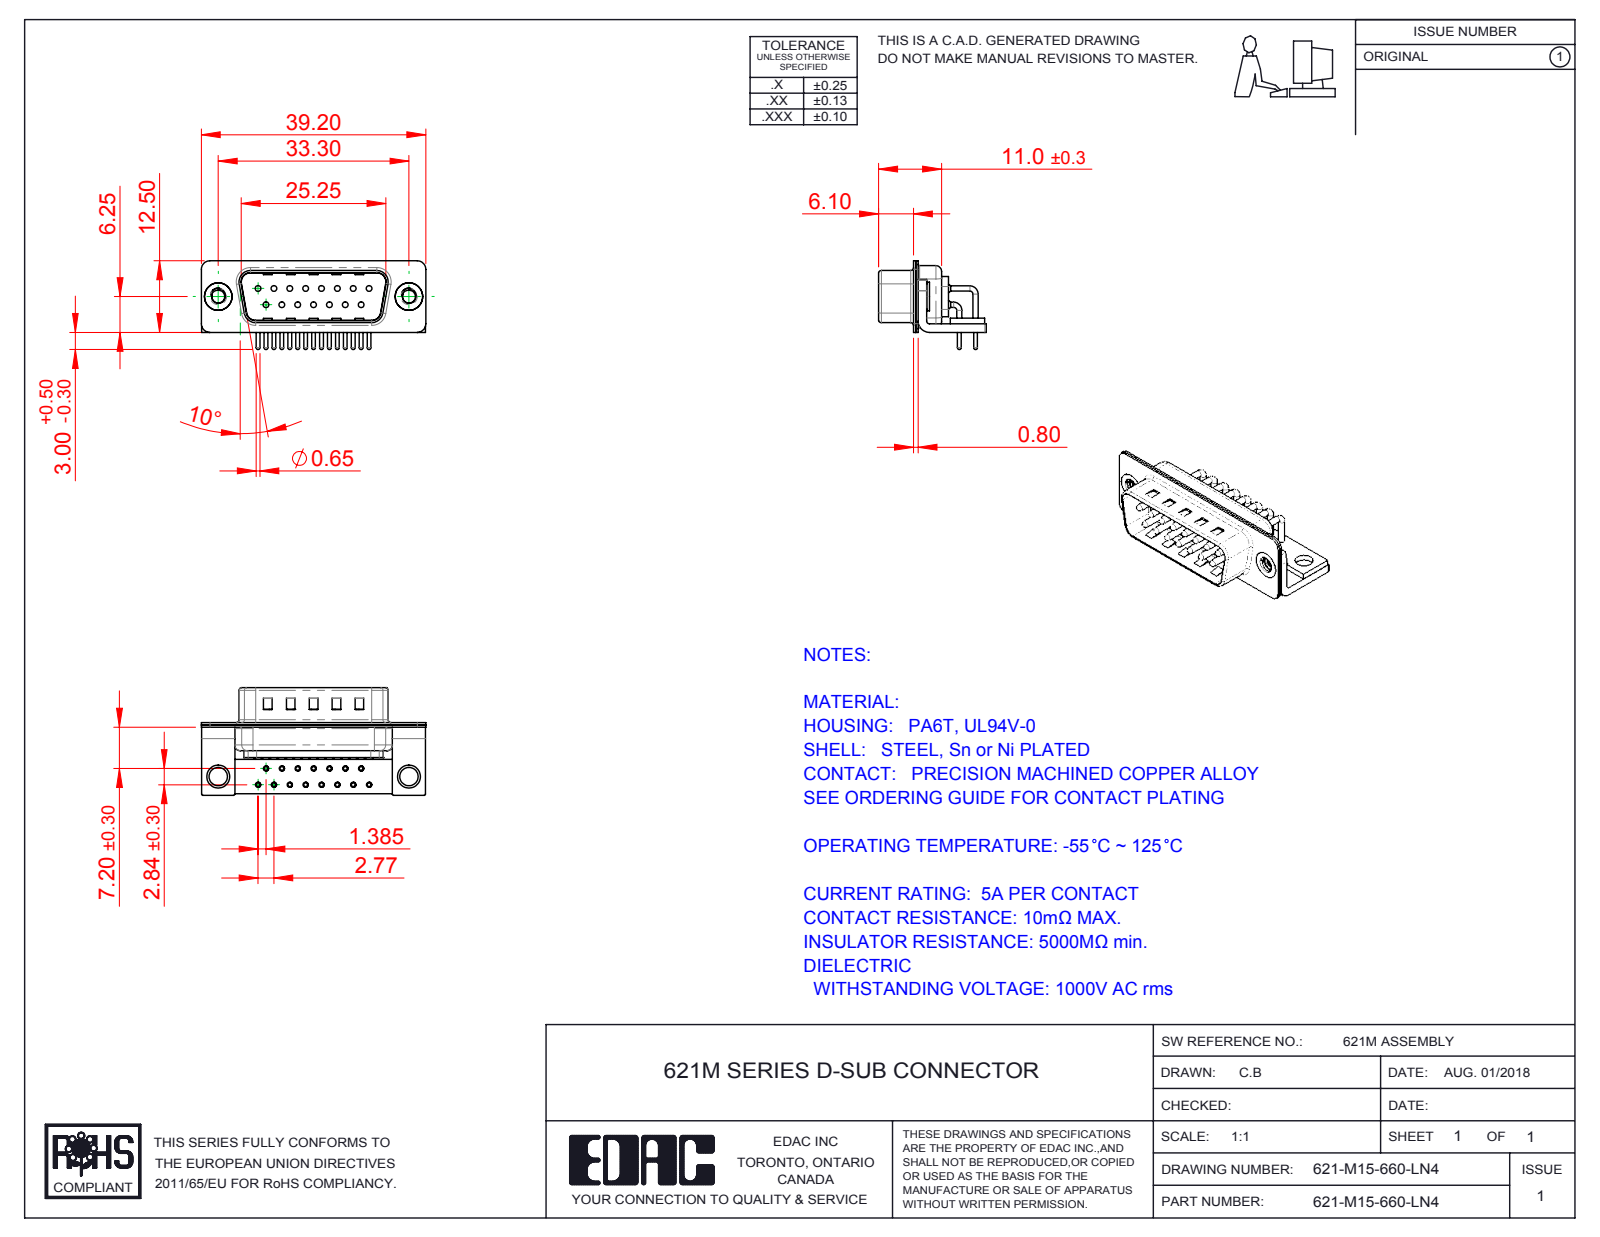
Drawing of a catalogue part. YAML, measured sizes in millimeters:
part_name: "621M Contact Row 2; 621M Shell Front_15 Contacts; 621M 4-40 Threaded Rivet_Stabilizer; 621M Housing_15 Contacts (+5 more)"
step_written_by: "SolidWorks 2016 (CONFIG_CONTROL_DESIGN)"
units: millimeters
bodies: {solids: 23, faces: 2070, planar: 1125, cylindrical: 725, other: 220}
overall_size: [39.2, 18.8, 15.49]
volume: 2371
surface_area: 6349
round_holes:
  - {diameter: 0.9, count: 15}
  - {diameter: 1, count: 15}
  - {diameter: 1.7, count: 15}
  - {diameter: 2, count: 15}
  - {diameter: 2.26, count: 2}
  - {diameter: 3.2, count: 2}
  - {diameter: 4, count: 2}
  - {diameter: 4.8, count: 2}
round_bosses_or_shafts:
  - {diameter: 0.9, count: 22}
  - {diameter: 1.5, count: 15}
  - {diameter: 0.65, count: 15}
  - {diameter: 5, count: 2}
  - {diameter: 4.9, count: 2}
partial_cylinders:
  - {radius: 0.25, count: 16}
  - {radius: 1.5, count: 16}
  - {radius: 1.01, count: 15}
  - {radius: 2, count: 13}
  - {radius: 0.5, count: 9}
  - {radius: 1.6, count: 8}
  - {radius: 0.6, count: 4}
  - {radius: 0.65, count: 4}
face_to_face_distances: [0.4, 0.85, 1.5, 0.8, 1.25, 10.4, 9.55, 1, 2.1, 1.9]
hole_center_spacings: [3.16, 2.77, 5.54, 8.31, 11.08, 5.03, 5.04, 7.48]
